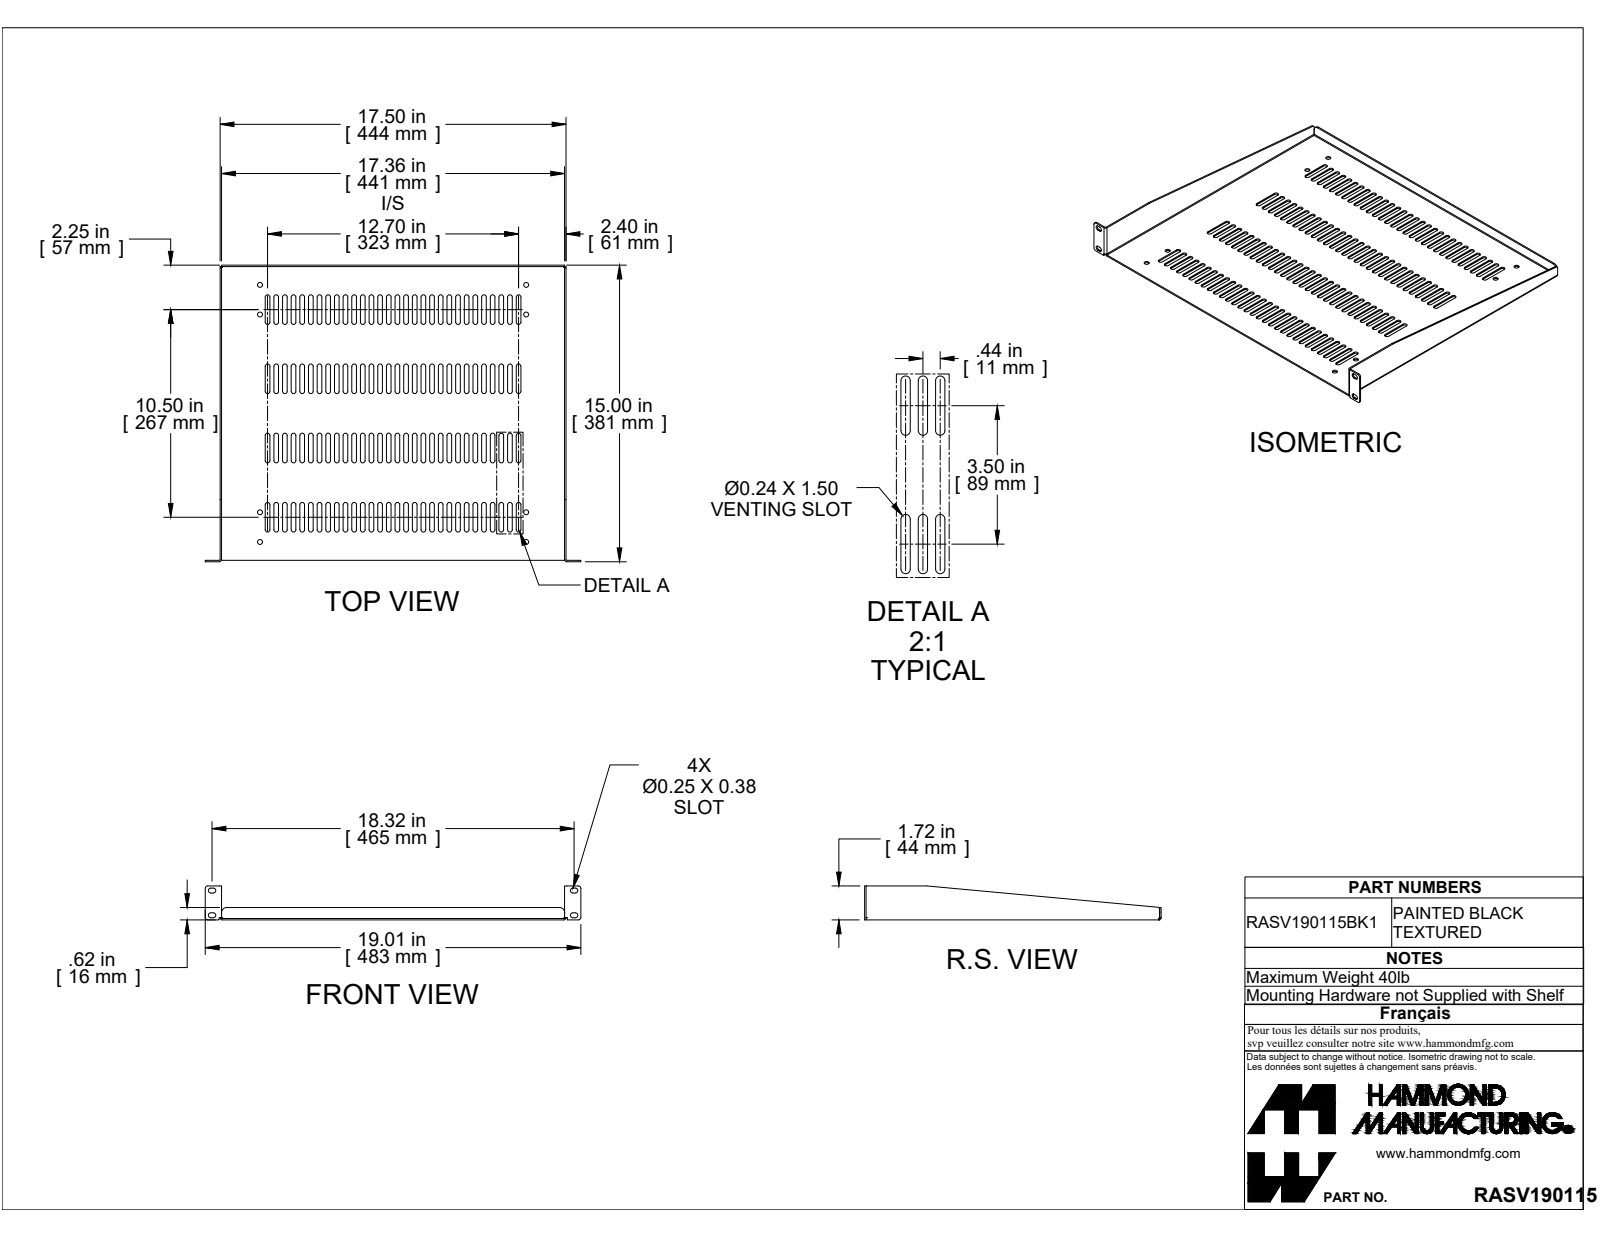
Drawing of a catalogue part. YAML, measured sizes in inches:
part_name: "RASV190115BK1"
step_written_by: "SolidWorks 2019 (CONFIG_CONTROL_DESIGN)"
units: inches
bodies: {solids: 1, faces: 568, planar: 288, cylindrical: 276, other: 4}
overall_size: [19.006, 15, 1.718]
volume: 19.19
surface_area: 567.4
round_holes:
  - {diameter: 0.25, count: 8}
partial_cylinders:
  - {radius: 0.118, count: 232}
  - {radius: 0.125, count: 12}
  - {radius: 0.117, count: 8}
  - {radius: 0.036, count: 5}
  - {radius: 0.108, count: 5}
  - {radius: 0.055, count: 3}
  - {radius: 0.25, count: 2}
face_to_face_distances: [0.072, 17.428, 17.356, 17.5, 0.876, 1.752, 14.856, 14.928, 2.19, 2.628]
hole_center_spacings: [1.5, 11.5, 13.468, 13.551, 17.709, 10, 13, 16.774]
